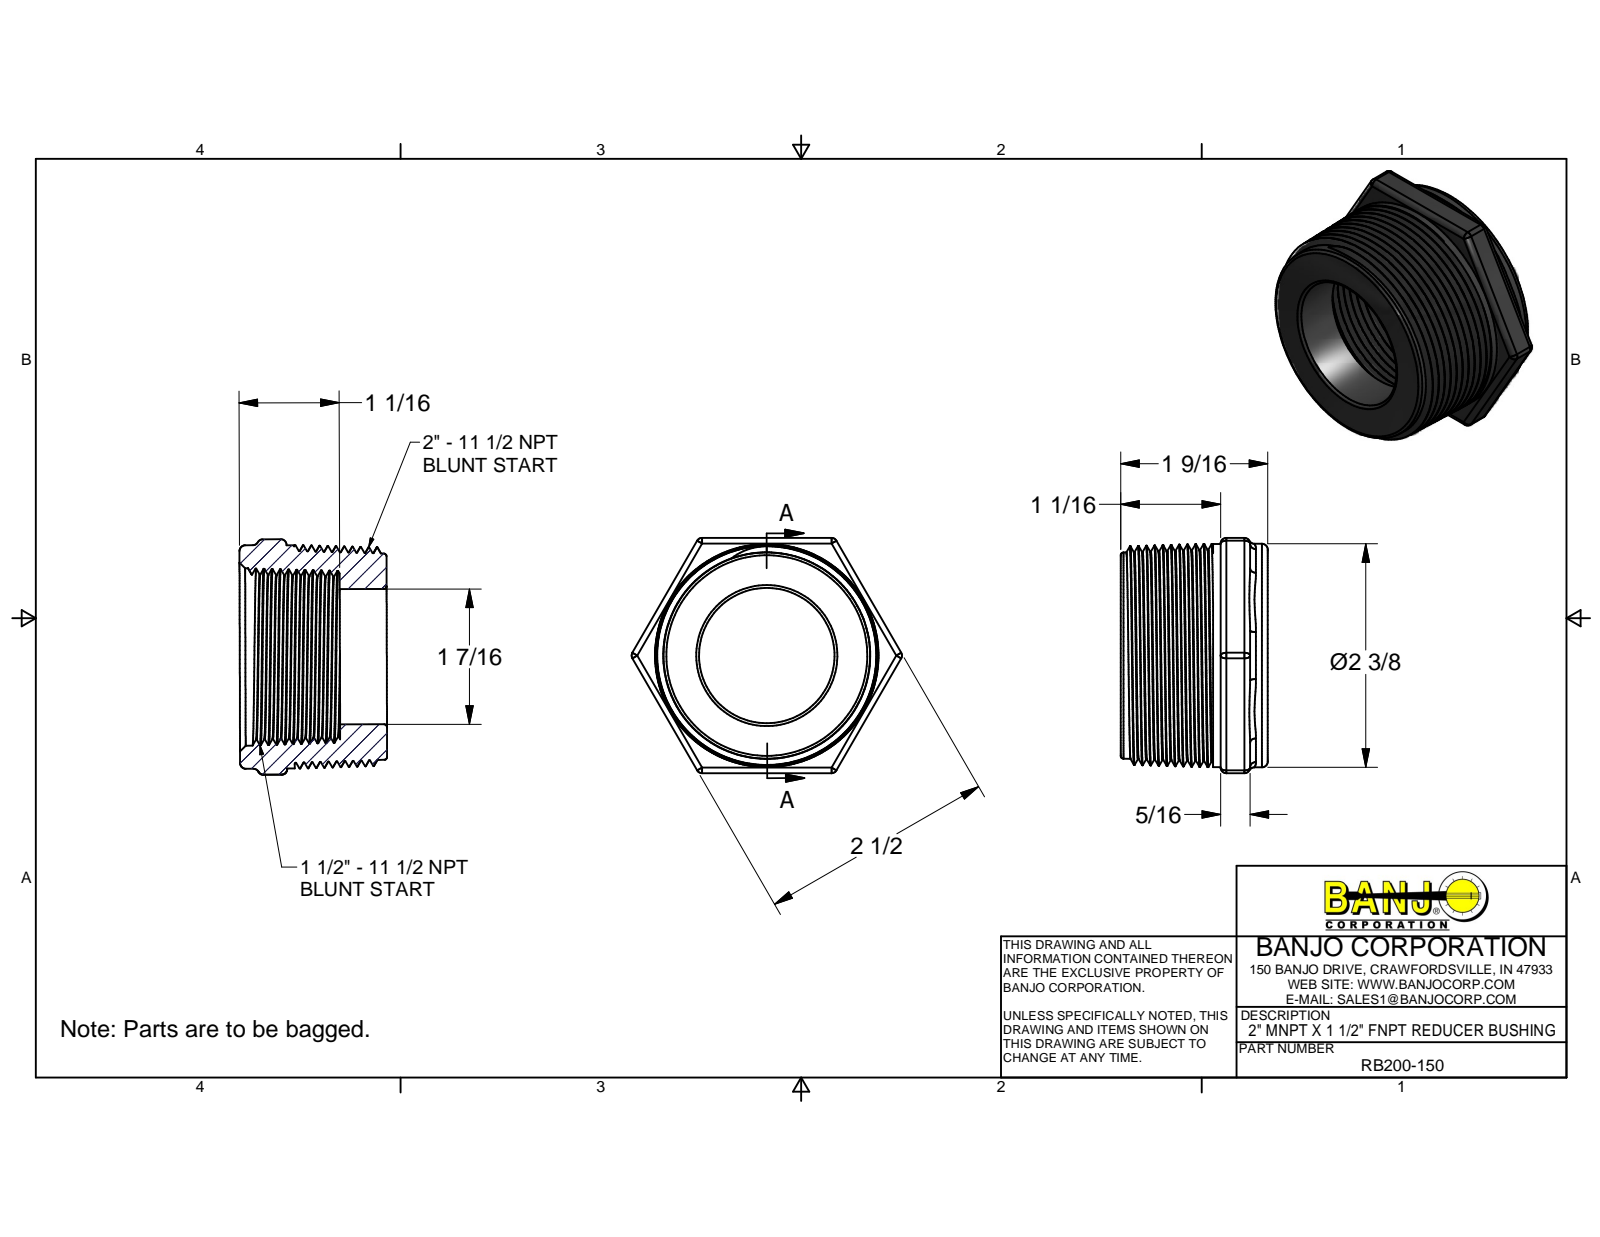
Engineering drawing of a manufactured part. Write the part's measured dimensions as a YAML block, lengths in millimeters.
part_name: "RB200-150"
step_written_by: "Autodesk Inventor 2014 (AUTOMOTIVE_DESIGN)"
units: millimeters
bodies: {solids: 1, faces: 103, planar: 17, cylindrical: 25, other: 61}
overall_size: [72.85, 63.5, 39.62]
volume: 54290
surface_area: 22756
round_holes:
  - {diameter: 36.51, count: 1}
round_bosses_or_shafts:
  - {diameter: 60.32, count: 1}
  - {diameter: 60.2, count: 1}
partial_cylinders:
  - {radius: 1.52, count: 18}
  - {radius: 13.59, count: 1}
  - {radius: 15.56, count: 1}
face_to_face_distances: [12.63, 26.99, 39.62, 63.5, 12.7, 14.29, 26.92, 14.73, 2.03, 12.26]
